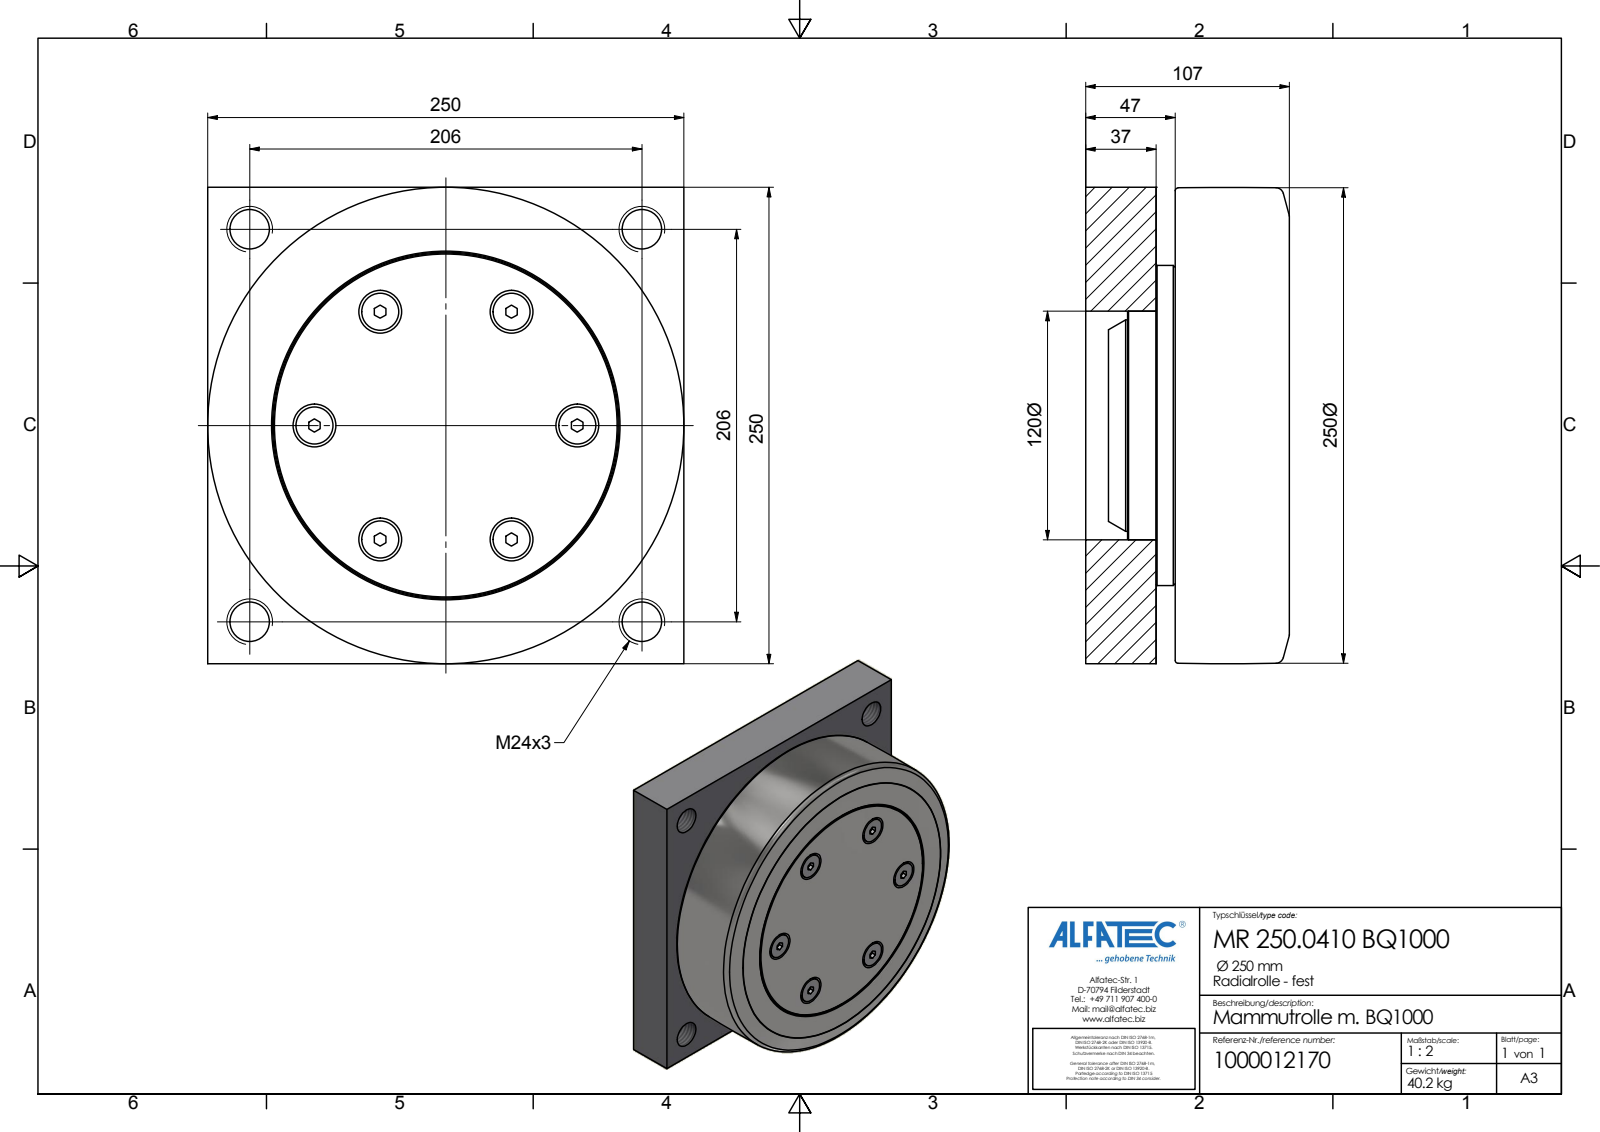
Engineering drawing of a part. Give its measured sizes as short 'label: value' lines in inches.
name: MR 250.0410 BQ1000_Kontur
written by: Autodesk Inventor 2020 (AUTOMOTIVE_DESIGN)
unit: in
bodies: 1 solid, 151 faces (77 planar, 29 cylindrical, 45 other)
size: 9.843 × 9.843 × 4.213
volume: 288.1 in³; area: 589.1 in²
holes: 4× ⌀0.817, 1× ⌀0.098, 1× ⌀0.194, 1× ⌀0.591, 1× ⌀4.724, 1× ⌀7.165, 1× ⌀7.795
bosses: 6× ⌀0.768, 1× ⌀7.126, 1× ⌀6.614, 1× ⌀6.102, 1× ⌀4.37, 1× ⌀0.118
rounds: 1× R0.138
face distances: 1.457, 1.85, 4.213, 2.756, 2.362, 0.394, 9.843, 0.512, 3.701, 2.244
hole spacings: 5.735, 8.11, 4.837, 6.811, 11.47, 1.417
